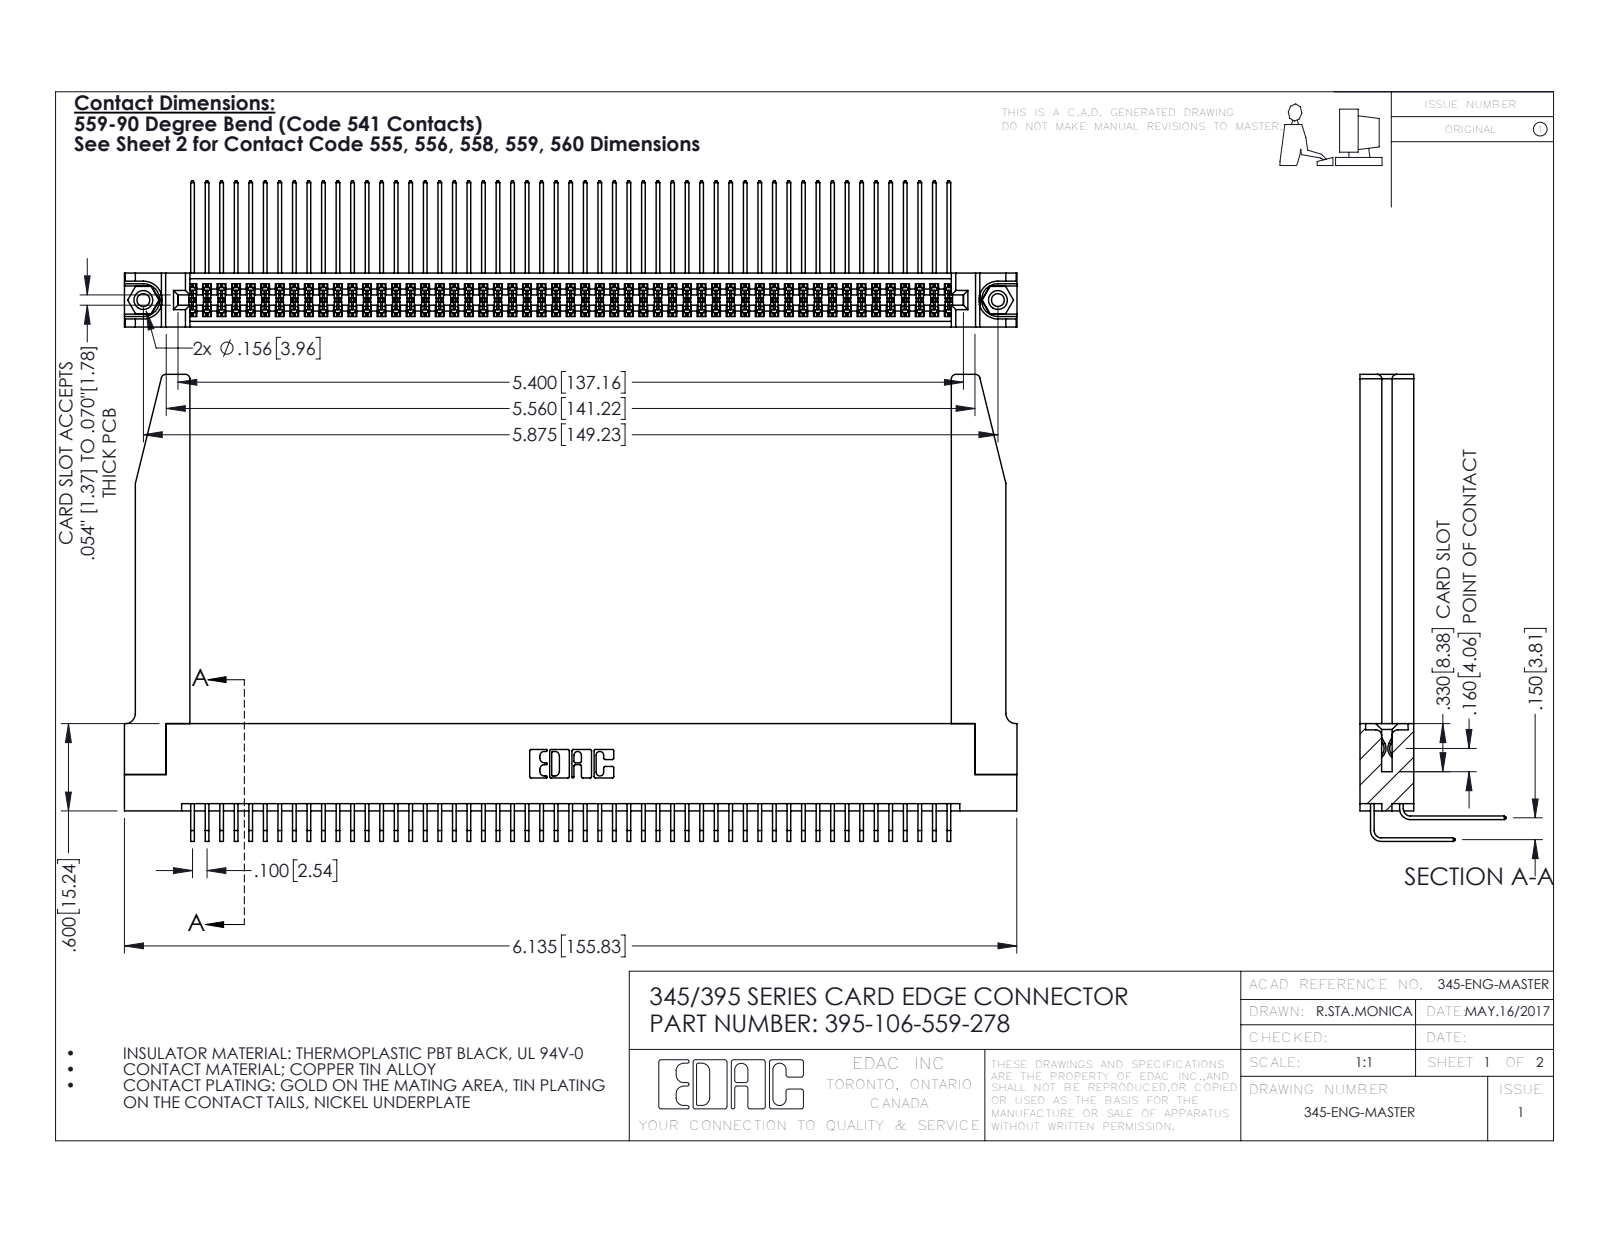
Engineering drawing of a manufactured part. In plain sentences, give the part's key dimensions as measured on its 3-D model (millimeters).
The part is named "345 Part_Flush Mounting Lugs - 0.156 Dia-TH; 395-106-559-278; 345-292-001_558 559 Tail - 1; 345-292-001_559 Tail - 2 (+2 more)". Its 3-D file was written by "SolidWorks 2016 (CONFIG_CONTROL_DESIGN)". It is 111 solids with 5872 faces: 3932 planar, 1888 cylindrical and 52 other. Overall it measures 155.9 by 81.5 by 25.5 millimeters. Its volume is 23 630 cubic millimeters and its surface area 33 360 square millimeters. Round holes: 2 of diameter 2.3, 2 of diameter 3.2, 2 of diameter 4, 1 of diameter 1.6. Round bosses or shafts: 2 of diameter 3.9. Partial cylindrical surfaces (rounded edges, fillets, slot ends): 159 of radius 0.2, 22 of radius 0.3, 8 of radius 0.8, 6 of radius 0.2, 6 of radius 0.8, 3 of radius 0.7, 2 of radius 0.4, 2 of radius 0.5. The main face-to-face distances are 1.8, 7.6, 9.4, 5.1, 2.5, 6.9, 0.6, 5.7, 4.4, 3.8. The hole center spacings are 6.9, 143.2, 149.2.
